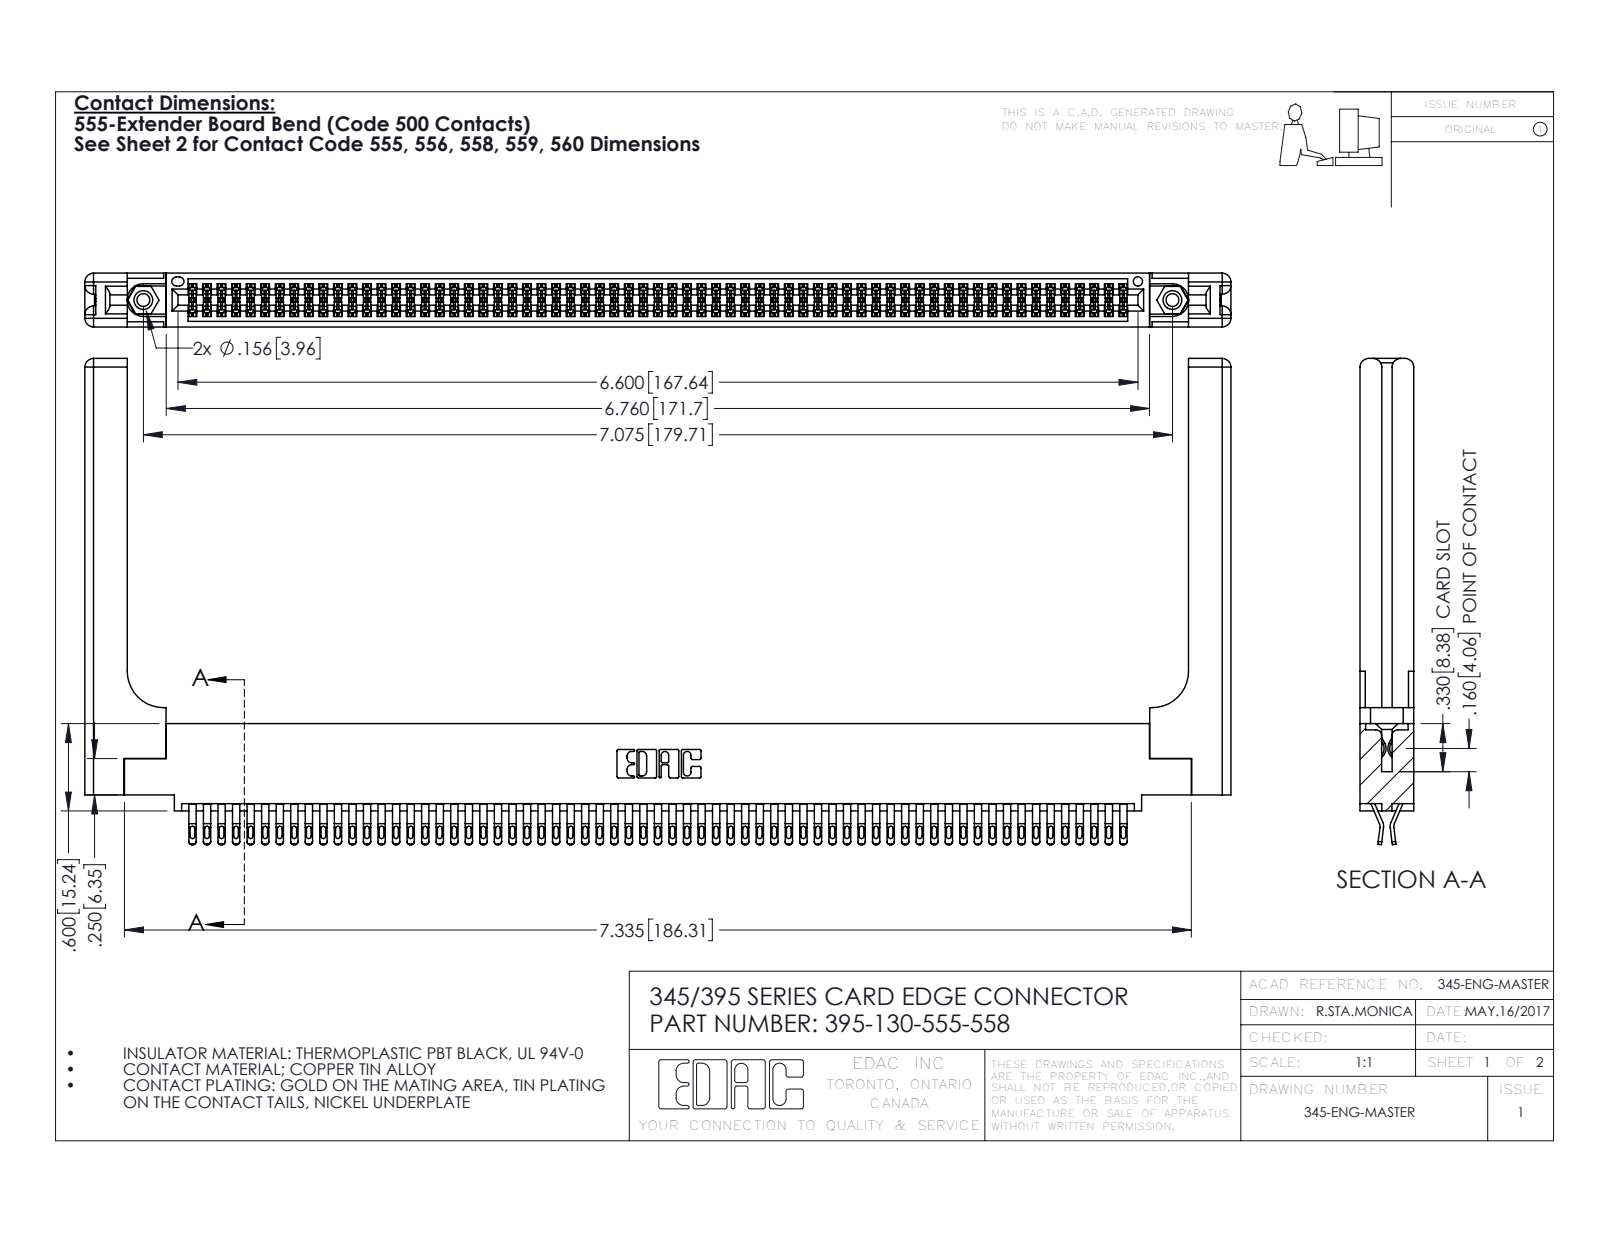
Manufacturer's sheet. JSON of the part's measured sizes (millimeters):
{"part_name": "345-292-001_555 Tail; 345-220-058_345-220-058; 345-250-001_345-250-001-102; 345 Part_0.110 Offset - 0.156 Dia-TH (+1 more)", "step_written_by": "SolidWorks 2016 (CONFIG_CONTROL_DESIGN)", "units": "millimeters", "bodies": {"solids": 135, "faces": 7666, "planar": 4262, "cylindrical": 3344, "other": 60}, "overall_size": [200.1, 84.9, 9.4], "volume_mm3": 28430, "surface_area_mm2": 36410, "round_holes": [[2.3, 2], [3.2, 2], [4, 2], [1.6, 1]], "round_bosses_or_shafts": [[3.9, 2]], "partial_cylinders_radius": [[0.4, 325], [0.5, 260], [0.2, 195], [0.3, 22], [1.5, 16], [0.2, 6], [0.8, 6], [0.7, 3]], "face_to_face_distances": [1.8, 7.6, 9.4, 0.6, 2.5, 6.9, 5.1, 5.7, 3.8, 3.8], "hole_center_spacings": [6.9, 173.7, 179.7]}
